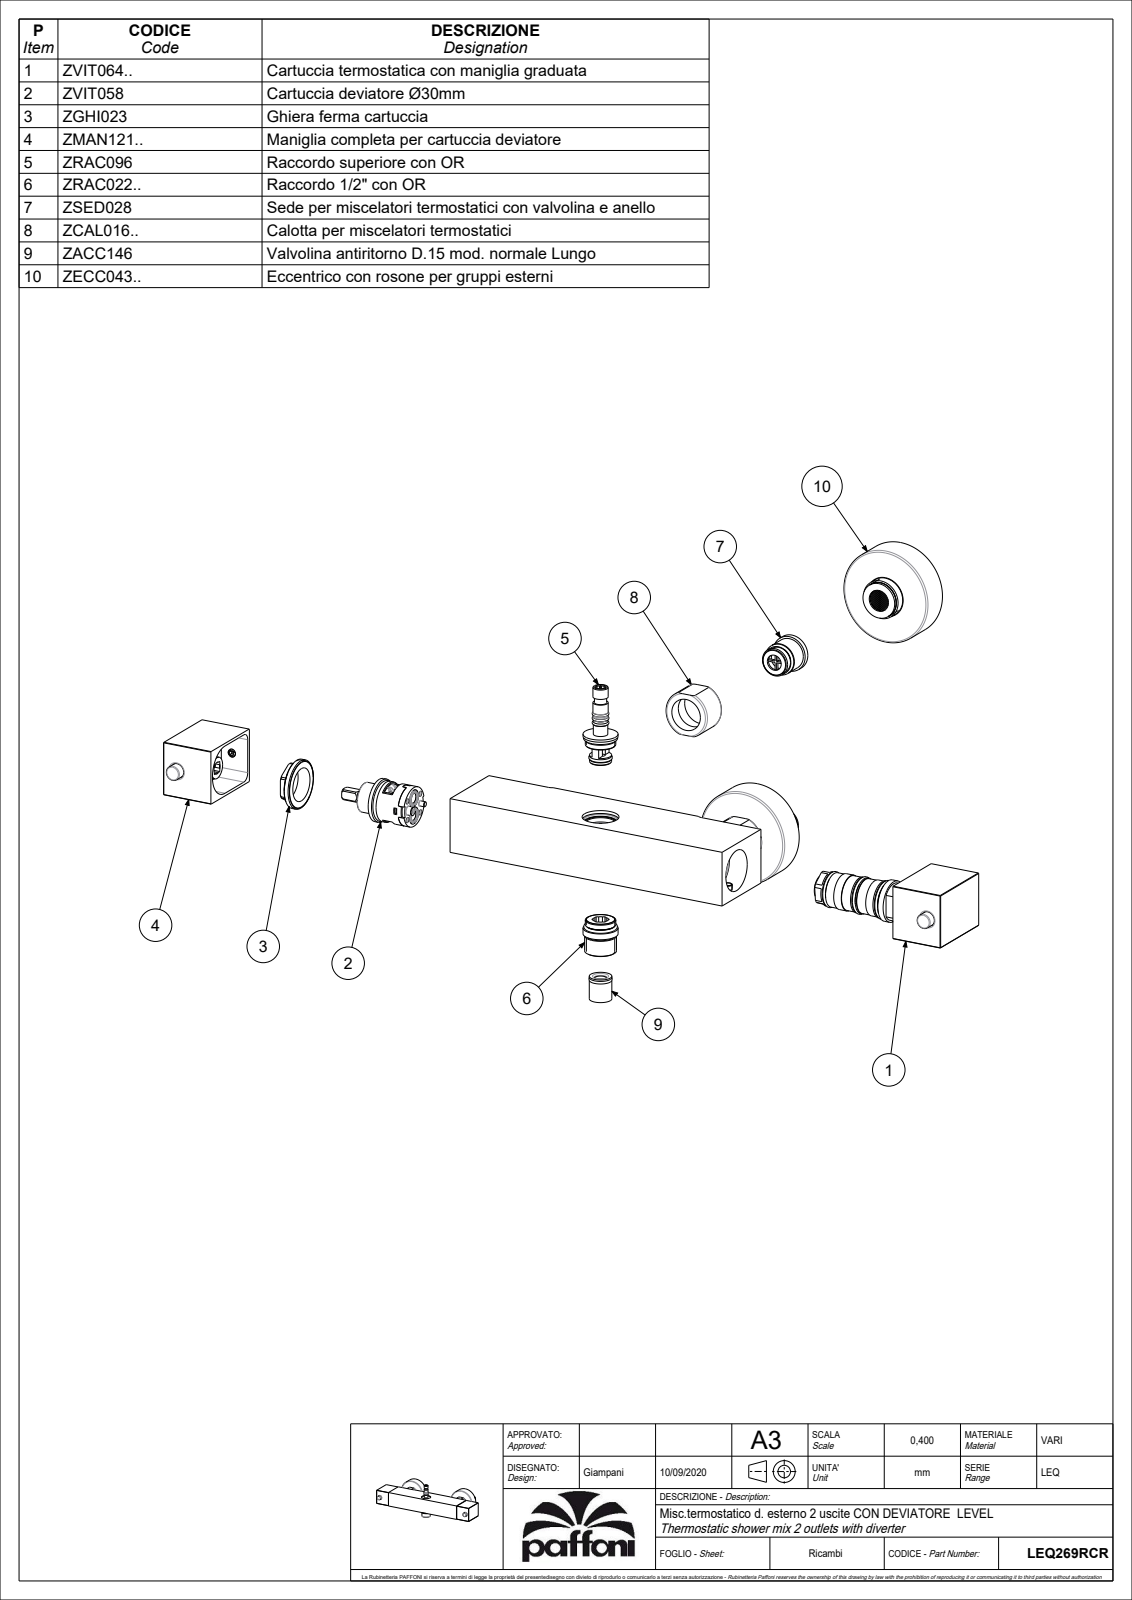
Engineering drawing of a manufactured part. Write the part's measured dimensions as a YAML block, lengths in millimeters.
part_name: "LEQ269RCR"
step_written_by: "CREO PARAMETRIC BY PTC INC, 2020044 (CONFIG_CONTROL_DESIGN)"
units: millimeters
bodies: {solids: 8, faces: 500, planar: 245, cylindrical: 153, other: 102}
overall_size: [279.05, 99.45, 84.5]
volume: 620778
surface_area: 104668
round_holes:
  - {diameter: 2.5, count: 2}
  - {diameter: 3, count: 2}
  - {diameter: 3.25, count: 2}
  - {diameter: 4, count: 2}
  - {diameter: 4.5, count: 2}
  - {diameter: 5.5, count: 2}
  - {diameter: 6.4, count: 2}
  - {diameter: 10.1, count: 2}
  - {diameter: 15.1, count: 2}
  - {diameter: 16, count: 2}
  - {diameter: 18, count: 2}
  - {diameter: 24.1, count: 2}
round_bosses_or_shafts:
  - {diameter: 63.5, count: 2}
  - {diameter: 24, count: 2}
  - {diameter: 21.2, count: 2}
  - {diameter: 9.8, count: 2}
  - {diameter: 7.6, count: 2}
  - {diameter: 23, count: 1}
  - {diameter: 20.9, count: 1}
  - {diameter: 14.5, count: 1}
partial_cylinders:
  - {radius: 5, count: 6}
  - {radius: 1.75, count: 2}
  - {radius: 4.82, count: 2}
  - {radius: 15.6, count: 2}
  - {radius: 16.5, count: 1}
face_to_face_distances: [37.5, 0.4, 37.1, 20, 94.7, 74.7, 43.7, 23.7, 51, 52]
hole_center_spacings: [4, 14, 14.05, 14.25, 40.4, 50.65, 54.4, 54.65]
